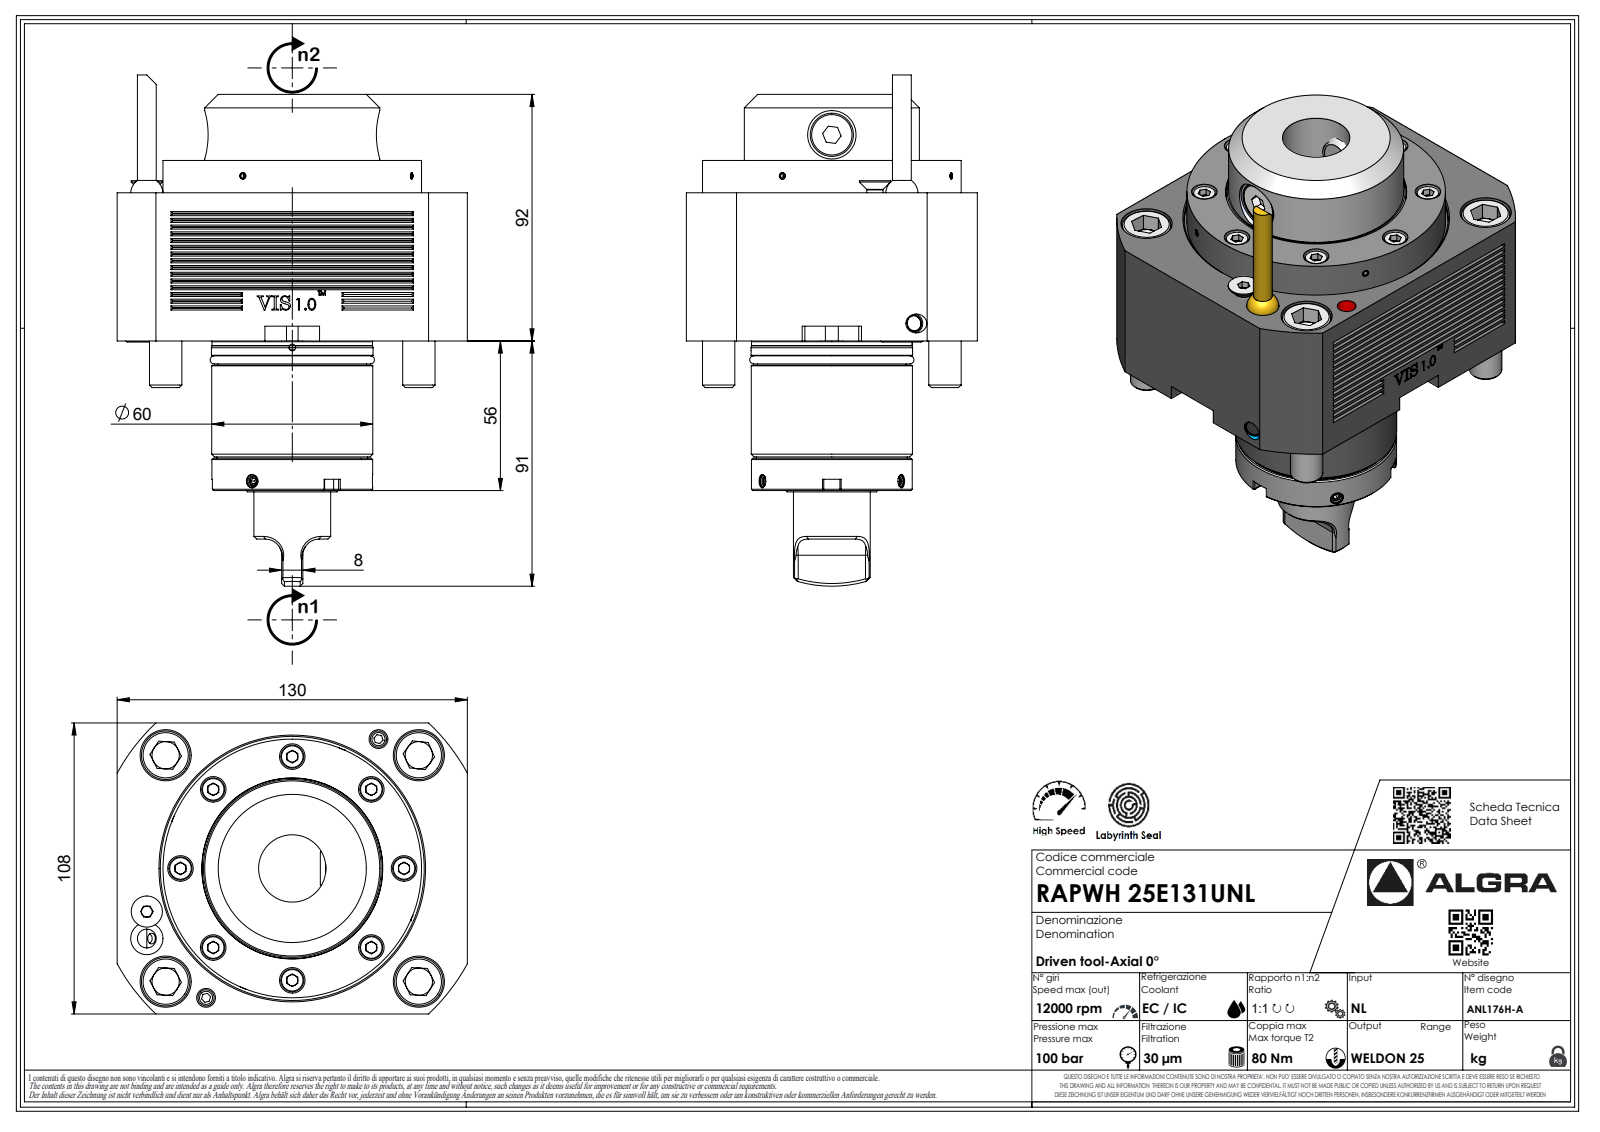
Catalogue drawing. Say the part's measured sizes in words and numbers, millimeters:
The part is named "RAPWH25E131UNL". Its 3-D file was written by "SolidWorks 2023 (AUTOMOTIVE_DESIGN)". It is 1 solid with 402 faces: 266 planar, 56 cylindrical and 80 other. Overall it measures 189.7 by 130 by 108 millimeters. Its volume is 1 085 000 cubic millimeters and its surface area 76 666 square millimeters. Round holes: 1 of diameter 2.1, 1 of diameter 4. Round bosses or shafts: 4 of diameter 12, 1 of diameter 96, 1 of diameter 65, 1 of diameter 60, 1 of diameter 28.5, 1 of diameter 7, 1 of diameter 6.37, 1 of diameter 1.7. Partial cylindrical surfaces (rounded edges, fillets, slot ends): 8 of radius 8, 7 of radius 0.33, 7 of radius 0.52, 7 of radius 3.7, 6 of radius 6, 1 of radius 0.21, 1 of radius 2, 1 of radius 46. The main face-to-face distances are 55, 108, 67, 12, 130, 91.5, 36.5, 24.5, 55.5, 110.5.
